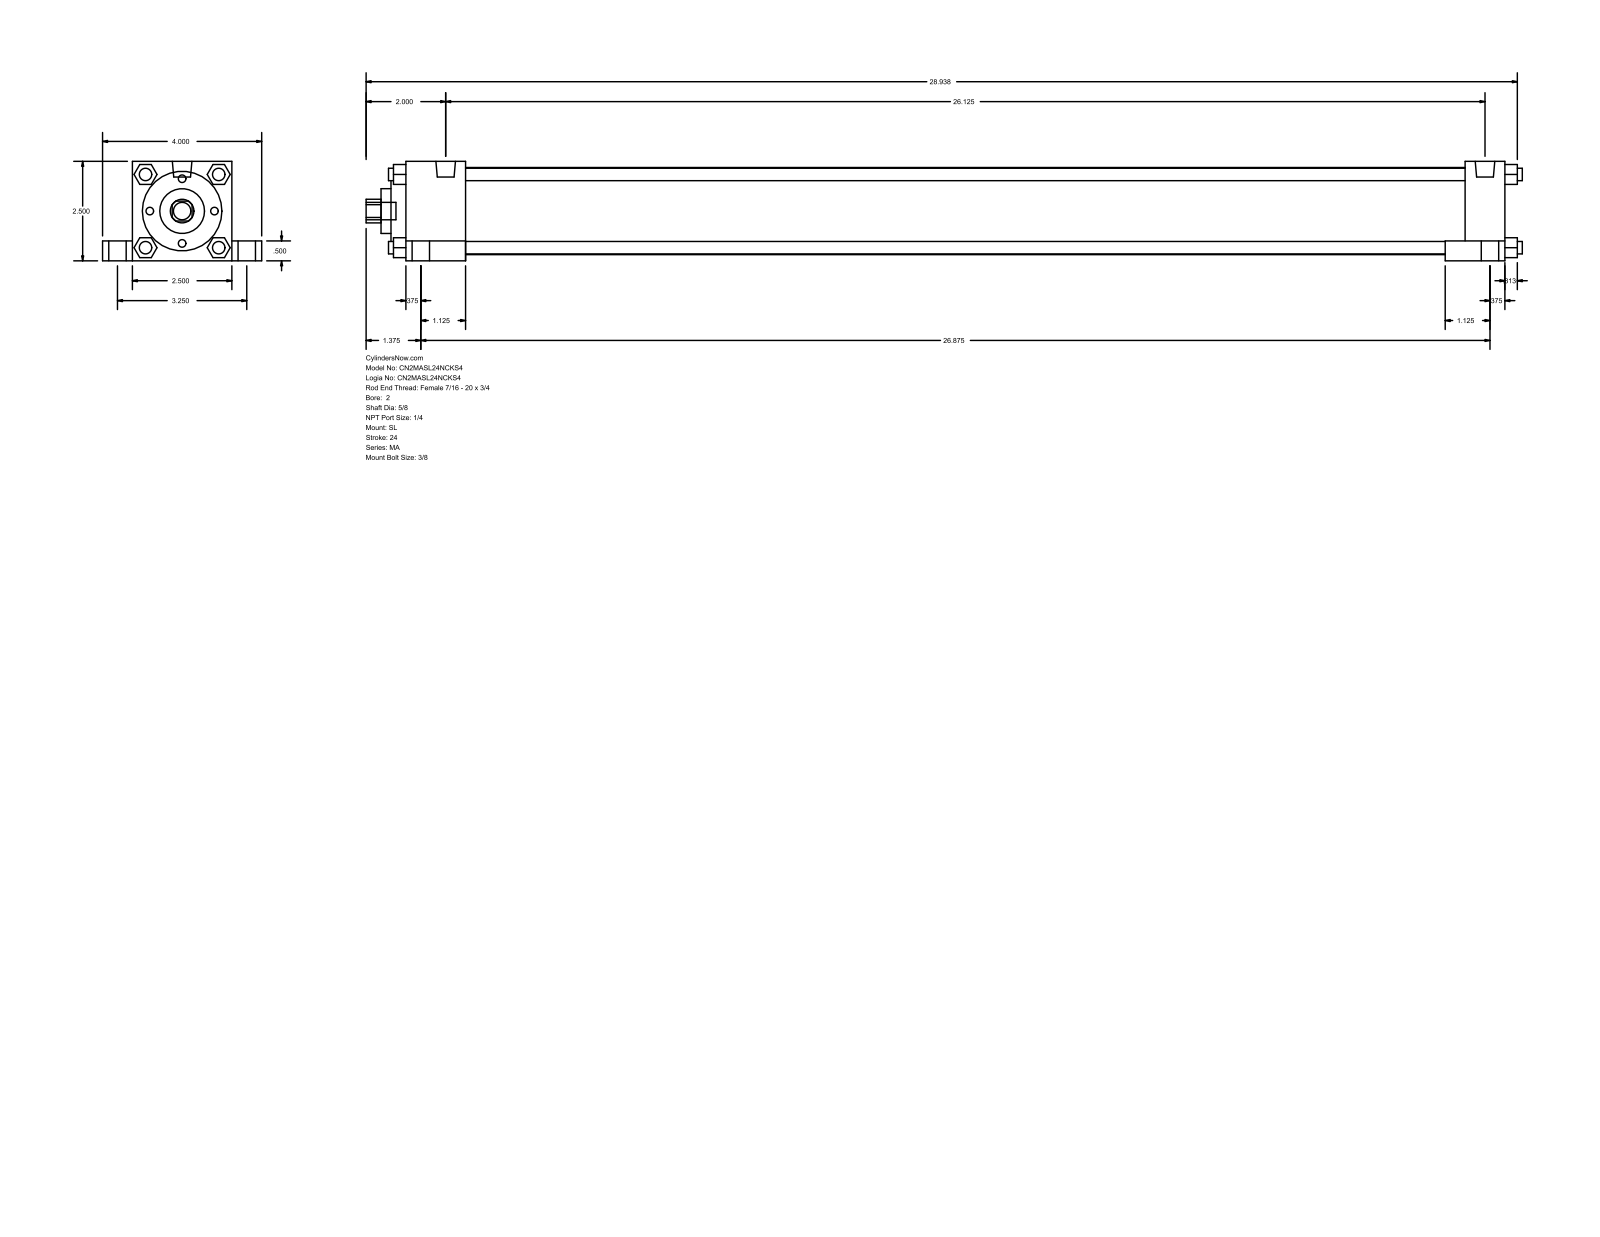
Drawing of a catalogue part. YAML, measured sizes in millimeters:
part_name: "MA_SL__0200_0.625"
step_written_by: "GSSL Pune (CONFIG_CONTROL_DESIGN)"
units: millimeters
bodies: {solids: 0, faces: 150, planar: 113, cylindrical: 37, other: 0}
overall_size: [738.19, 101.6, 63.5]
round_holes:
  - {diameter: 15.88, count: 1}
  - {diameter: 28.57, count: 1}
  - {diameter: 50.8, count: 1}
  - {diameter: 55.63, count: 1}
round_bosses_or_shafts:
  - {diameter: 7.94, count: 8}
  - {diameter: 11.11, count: 5}
  - {diameter: 17.46, count: 4}
  - {diameter: 12.49, count: 2}
partial_cylinders:
  - {radius: 7.54, count: 1}
face_to_face_distances: [63.5, 12.7, 9.52, 638.17, 19.05, 82.55, 38.1, 50.8, 701.68, 663.58]
